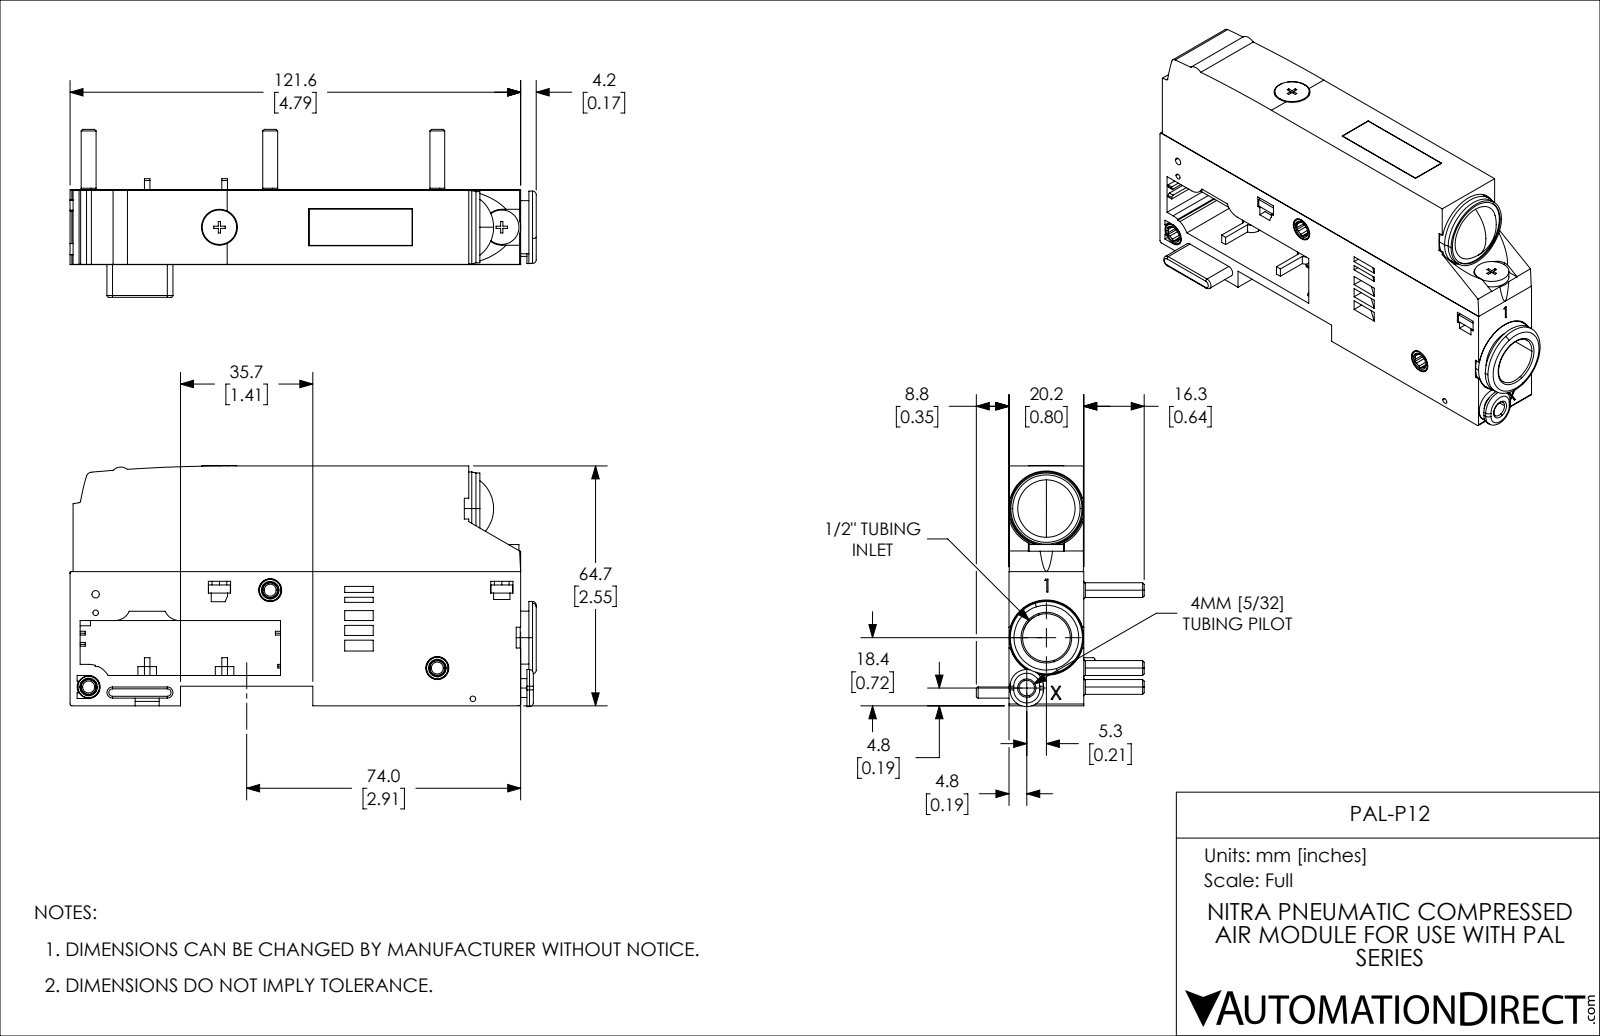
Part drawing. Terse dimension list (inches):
name: PAL-P12
written by: SolidWorks 2019 (CONFIG_CONTROL_DESIGN)
unit: in
bodies: 4 solids, 1135 faces (914 planar, 163 cylindrical, 58 other)
size: 4.953 × 2.559 × 1.783
volume: 7.455 in³; area: 57.9 in²
holes: 3× ⌀0.128, 3× ⌀0.157, 3× ⌀0.165, 2× ⌀0.059, 2× ⌀0.079, 2× ⌀0.177, 2× ⌀0.244, 1× ⌀0.126, 1× ⌀0.189, 1× ⌀0.362, 1× ⌀0.374, 1× ⌀0.382
bosses: 5× ⌀0.157, 3× ⌀0.366, 3× ⌀0.236, 1× ⌀0.787, 1× ⌀0.78, 1× ⌀0.768, 1× ⌀0.756, 1× ⌀0.563
rounds: 11× R0.02, 4× R0.039, 3× R0.059, 3× R0.082, 2× R0.031, 2× R0.098, 2× R0.157, 2× R0.165
face distances: 0.791, 0.787, 0.795, 2.547, 0.323, 0.583, 1.642, 0.906, 0.209, 2.224
hole spacings: 0.172, 0.197, 0.22, 0.221, 0.234, 0.356, 0.356, 0.488
